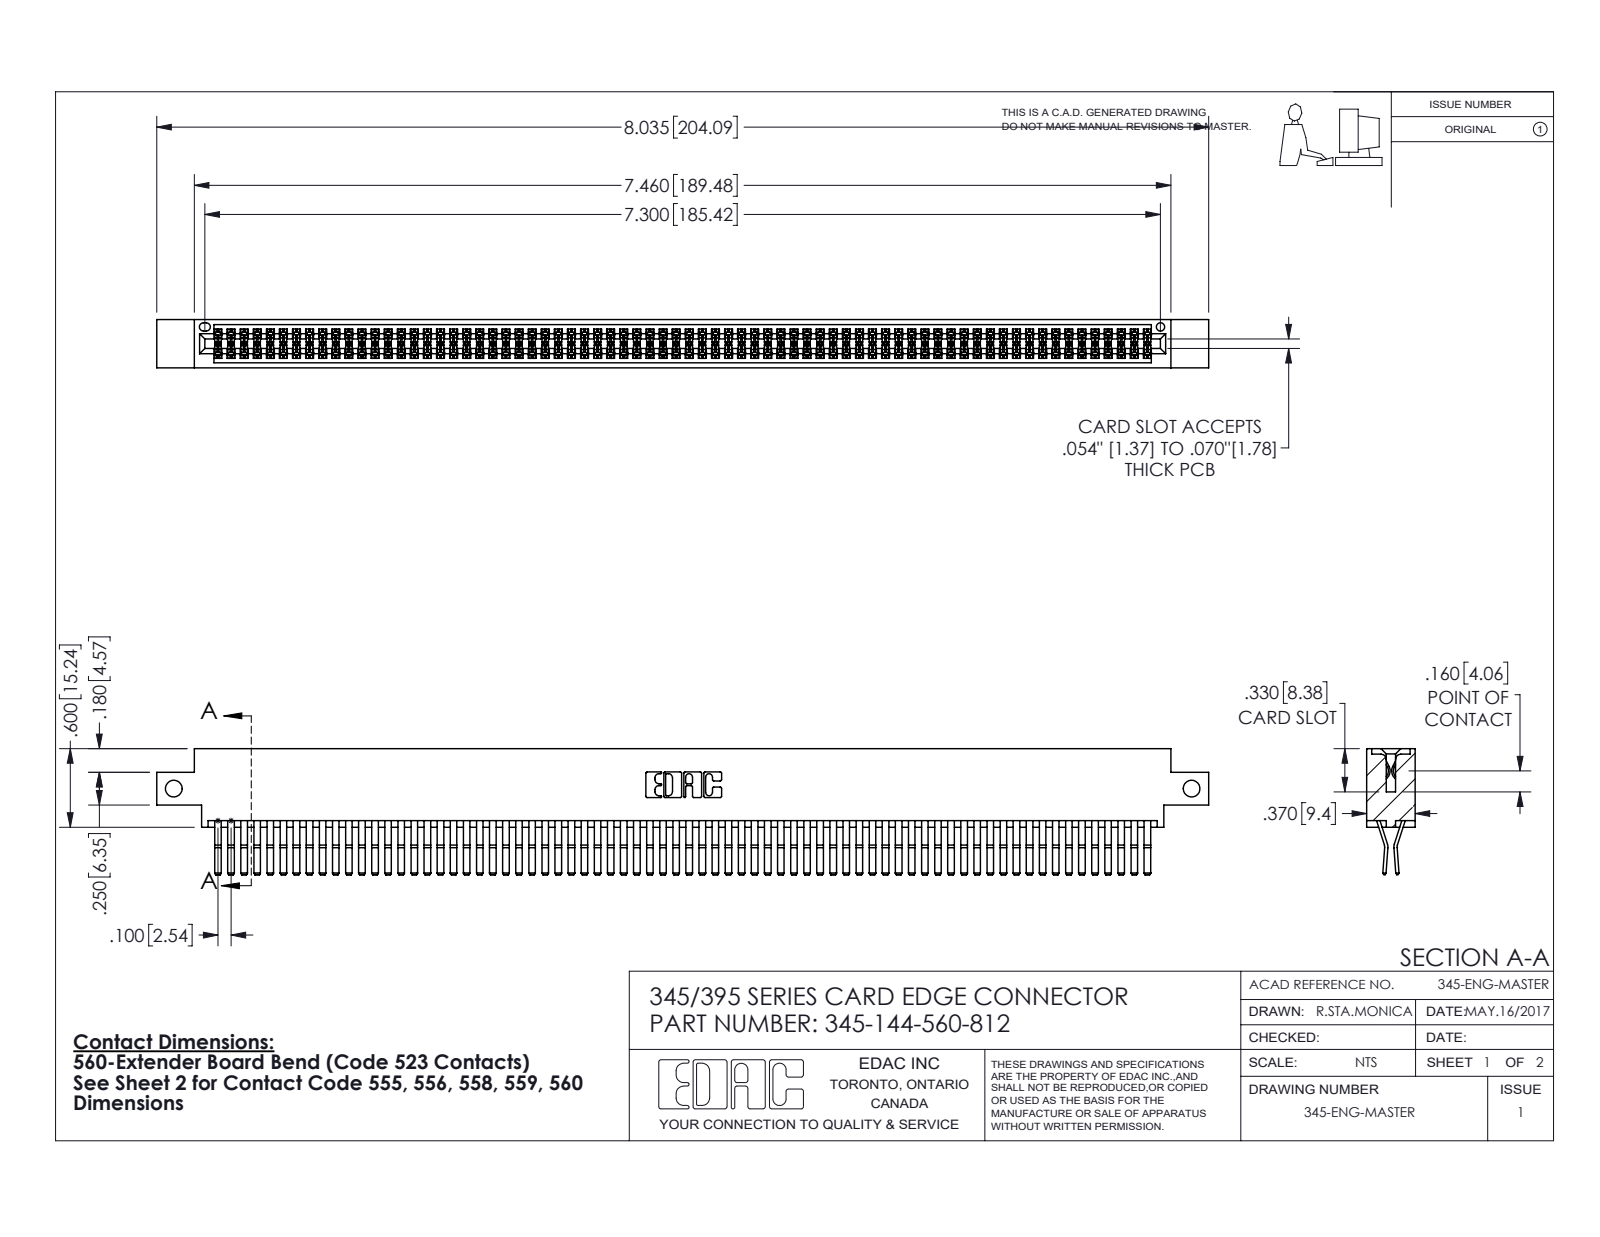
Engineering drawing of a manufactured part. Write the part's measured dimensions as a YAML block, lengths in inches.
part_name: "345-144-560-812; 345-292-001_560 Tail; 345 Part_0.170 Offset - Side Mount"
step_written_by: "SolidWorks 2016 (CONFIG_CONTROL_DESIGN)"
units: inches
bodies: {solids: 145, faces: 7618, planar: 4836, cylindrical: 2782, other: 0}
overall_size: [8.035, 0.962, 0.37]
volume: 1.272
surface_area: 52.44
round_holes:
  - {diameter: 0.128, count: 2}
  - {diameter: 0.064, count: 1}
partial_cylinders:
  - {radius: 0.006, count: 217}
  - {radius: 0.01, count: 22}
  - {radius: 0.007, count: 6}
  - {radius: 0.031, count: 6}
  - {radius: 0.026, count: 3}
  - {radius: 0.01, count: 2}
  - {radius: 0.014, count: 2}
  - {radius: 0.019, count: 2}
face_to_face_distances: [0.025, 0.298, 0.072, 0.37, 0.2, 0.098, 0.272, 0.225, 0.175, 0.149]
hole_center_spacings: [7.775]
